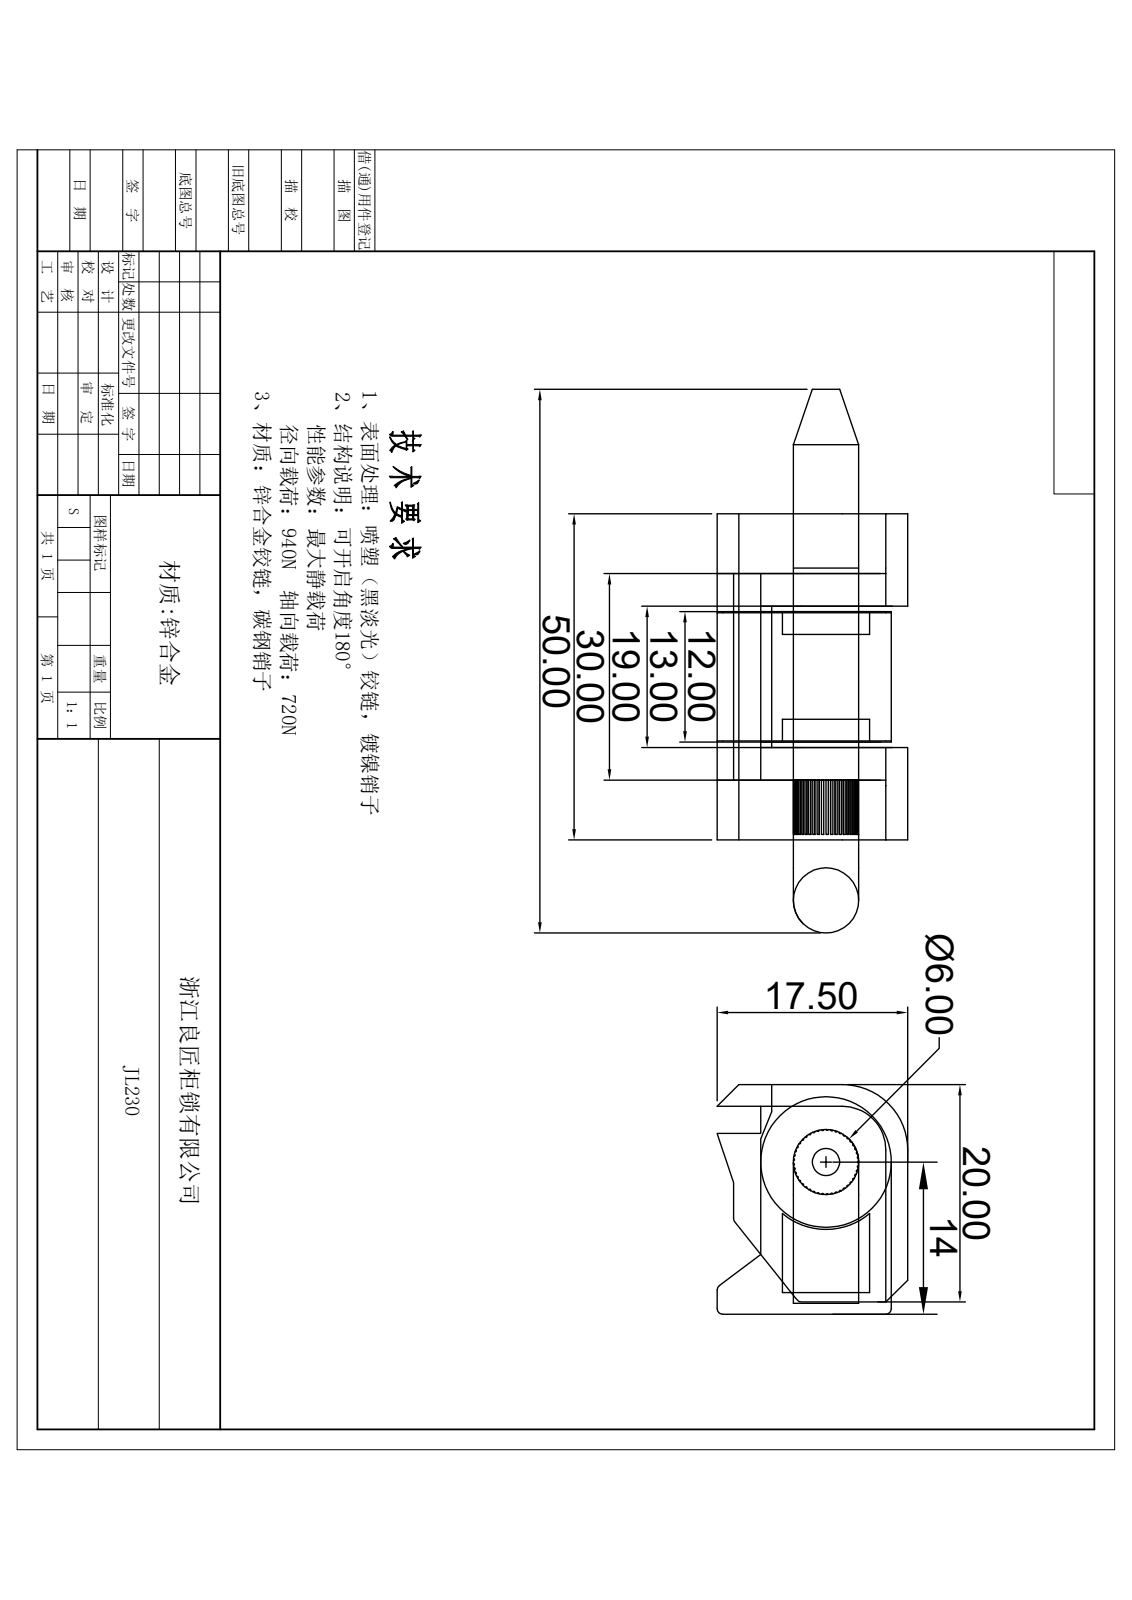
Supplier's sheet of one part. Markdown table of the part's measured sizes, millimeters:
| quantity | value |
| --- | --- |
| STEP written by | Rhino 8.5 (CONFIG_CONTROL_DESIGN) |
| units | millimeters |
| bodies | 3 solids, 218 faces (141 planar, 73 cylindrical, 4 other) |
| overall size | 50 × 21.12 × 17.5 |
| volume | 6 627 mm³ |
| surface area | 5 521 mm² |
| round holes (diameter × count) | 6 × 1 |
| round bosses / shafts (diameter × count) | 12 × 1, 6 × 1 |
| partial cylindrical surfaces (radius × count) | 0.1 × 45, 0.5 × 6, 4 × 1, 6 × 1, 6.2 × 1 |
| main face-to-face distances | 2, 16, 3, 0.5, 12, 15.5, 3.5, 12.5, 13, 1.5 |
